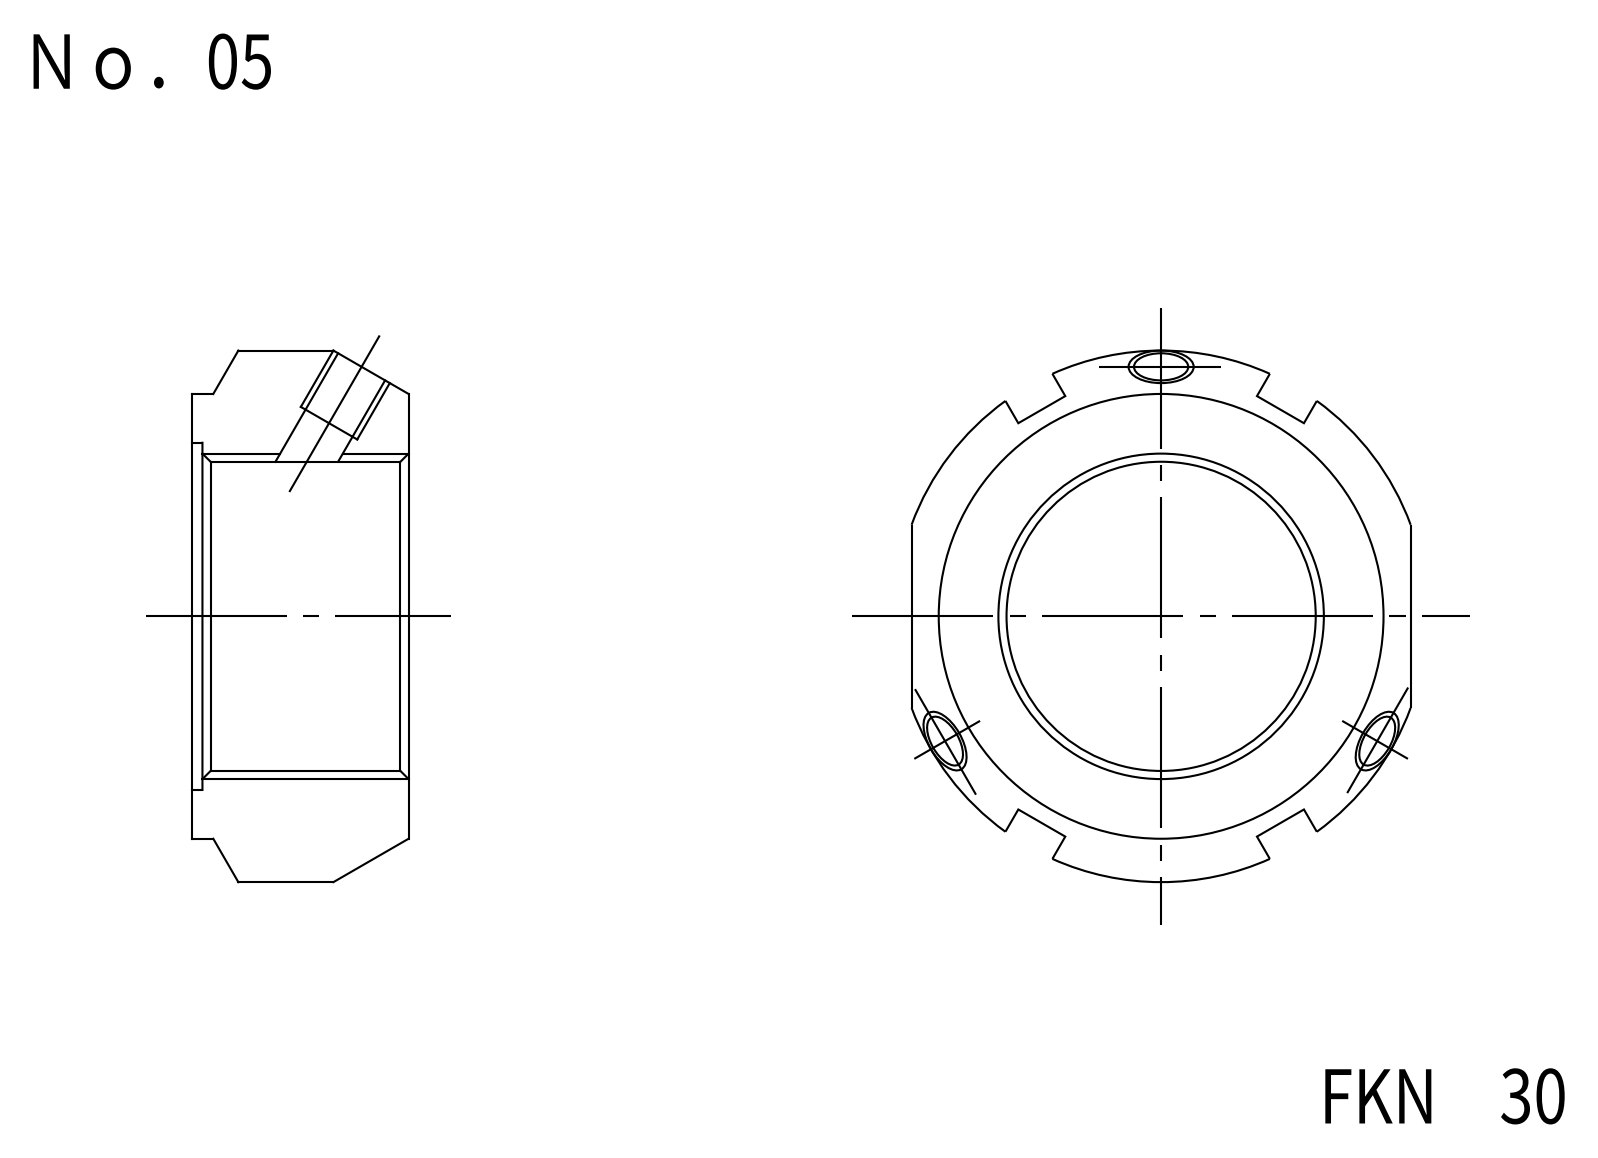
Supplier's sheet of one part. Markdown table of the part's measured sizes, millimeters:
| quantity | value |
| --- | --- |
| part name | FKD FKN30 |
| STEP written by | Autodesk Inventor LT (CONFIG_CONTROL_DESIGN) |
| units | millimeters |
| bodies | 1 solid, 37 faces (20 planar, 15 cylindrical, 2 other) |
| overall size | 49 × 46 × 20 |
| volume | 18 210 mm³ |
| surface area | 6 922 mm² |
| round holes (diameter × count) | 6.1 × 3, 4.92 × 2, 4.92 × 1, 30 × 1, 32 × 1 |
| round bosses / shafts (diameter × count) | 41 × 1 |
| partial cylindrical surfaces (radius × count) | 24.5 × 1 |
| main face-to-face distances | 20, 46, 44, 5, 1.5, 18.5 |
